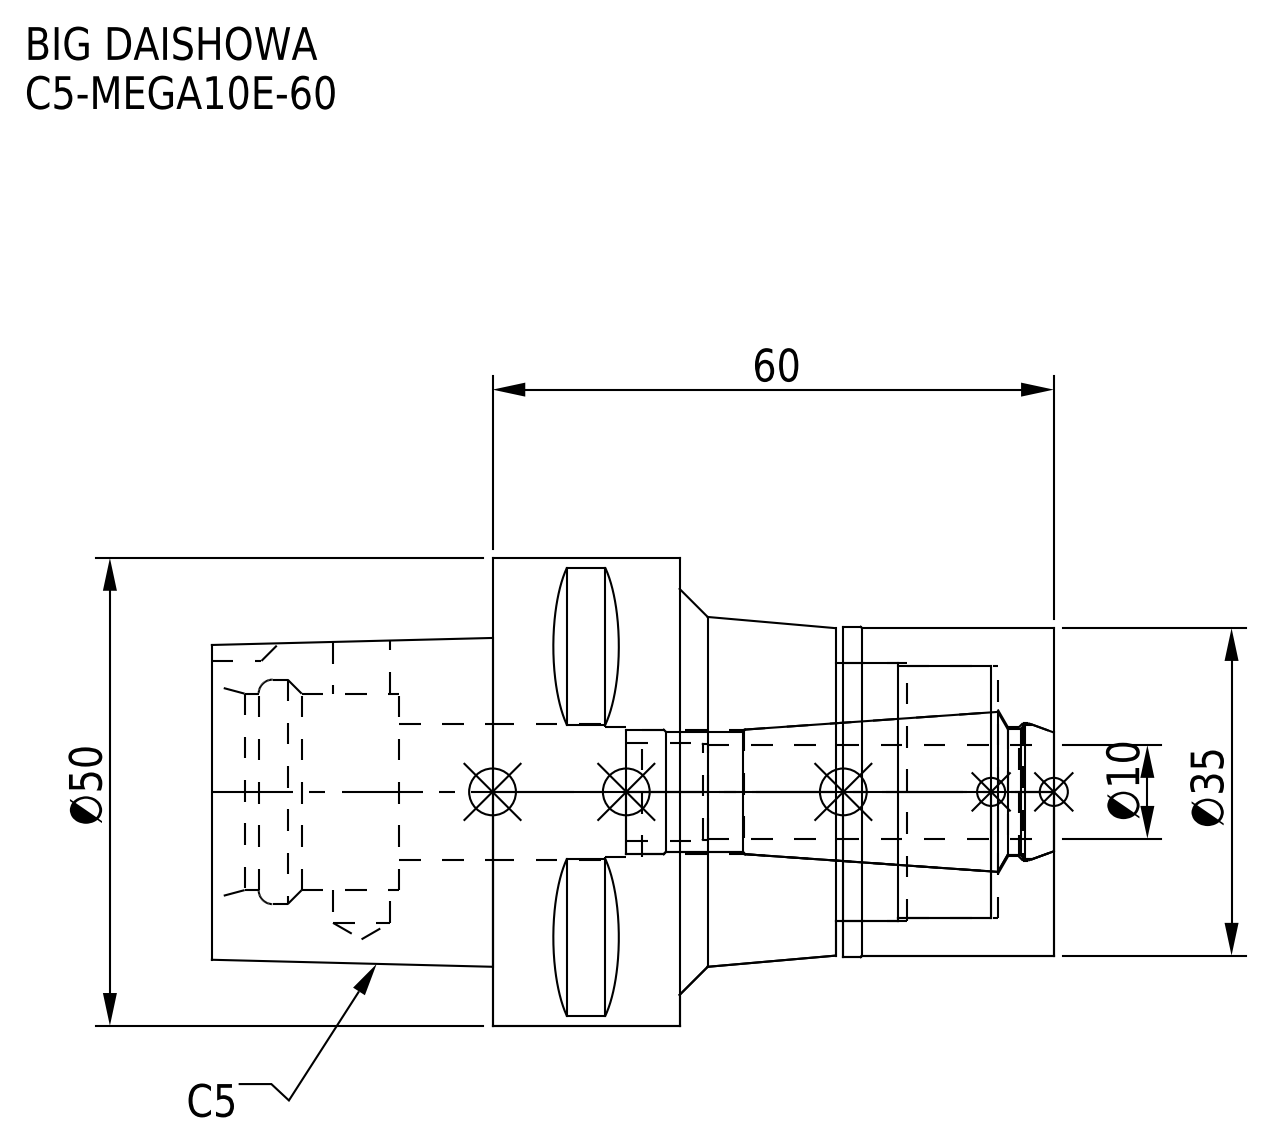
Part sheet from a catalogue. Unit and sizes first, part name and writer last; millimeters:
Units: millimetres
Overall size (bounding box): 90 × 50 × 50
Round holes (diameter × count): ⌀6.1 ×1, ⌀13.3 ×1, ⌀13.8 ×1, ⌀13.9 ×1, ⌀14.5 ×1, ⌀14.7 ×1, ⌀21 ×1, ⌀24 ×1, ⌀27 ×1, ⌀27.5 ×1
Round bosses / shafts (diameter × count): ⌀50 ×1, ⌀35.3 ×1, ⌀35 ×1
Partial cylindrical surfaces — rounded edges, fillets, slot ends (radius × count): R4 ×1
Main face-to-face distances: 60, 20, 30, 40, 16.7, 23.3, 22.5, 17.5, 37.5, 90
Volume: 86 312 mm³ · Surface area: 23 302 mm²
Bodies: 2 solids, 94 faces (35 planar, 35 cylindrical, 24 other)
Part name (STEP PRODUCT): C5-MEGA10E-60_1.stp; C5-MEGA10E-60-100-FreeParts; C5-MEGA10E-60-100_ASM.stp; C5-MEGA10E-60-100.stp (+3 more)
STEP written by: SolidWorks 2019 (CONFIG_CONTROL_DESIGN)
